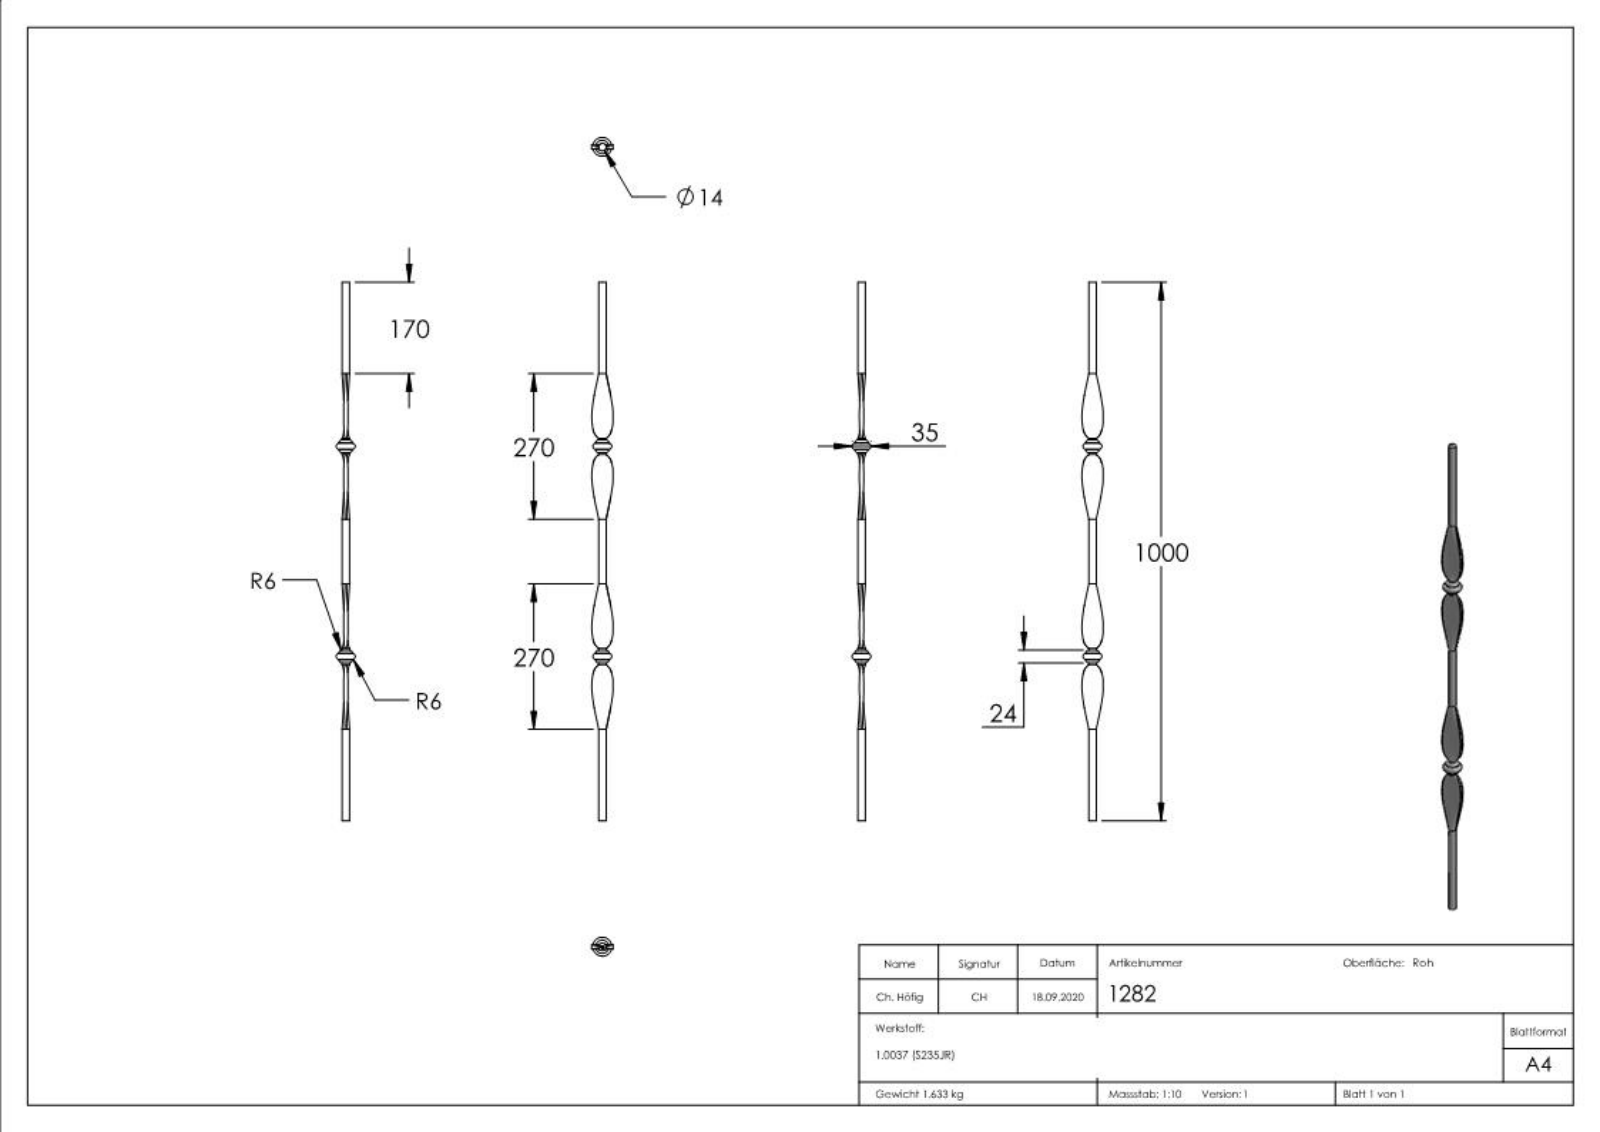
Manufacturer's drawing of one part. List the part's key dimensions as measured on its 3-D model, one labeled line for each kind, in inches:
Part name (STEP PRODUCT): 1282
STEP written by: SolidWorks 2018 (CONFIG_CONTROL_DESIGN)
Units: inches
Bodies: 1 solid, 218 faces (91 planar, 22 cylindrical, 105 other)
Overall size (bounding box): 39.37 × 1.571 × 1.378
Volume: 12.78 in³ · Surface area: 98.27 in²
Round bosses / shafts (diameter × count): ⌀0.984 ×1, ⌀0.551 ×1
Main face-to-face distances: 39.37, 39.366, 0.07, 0.033, 0.064, 0.119, 0.039, 0.016, 0.087, 0.026
